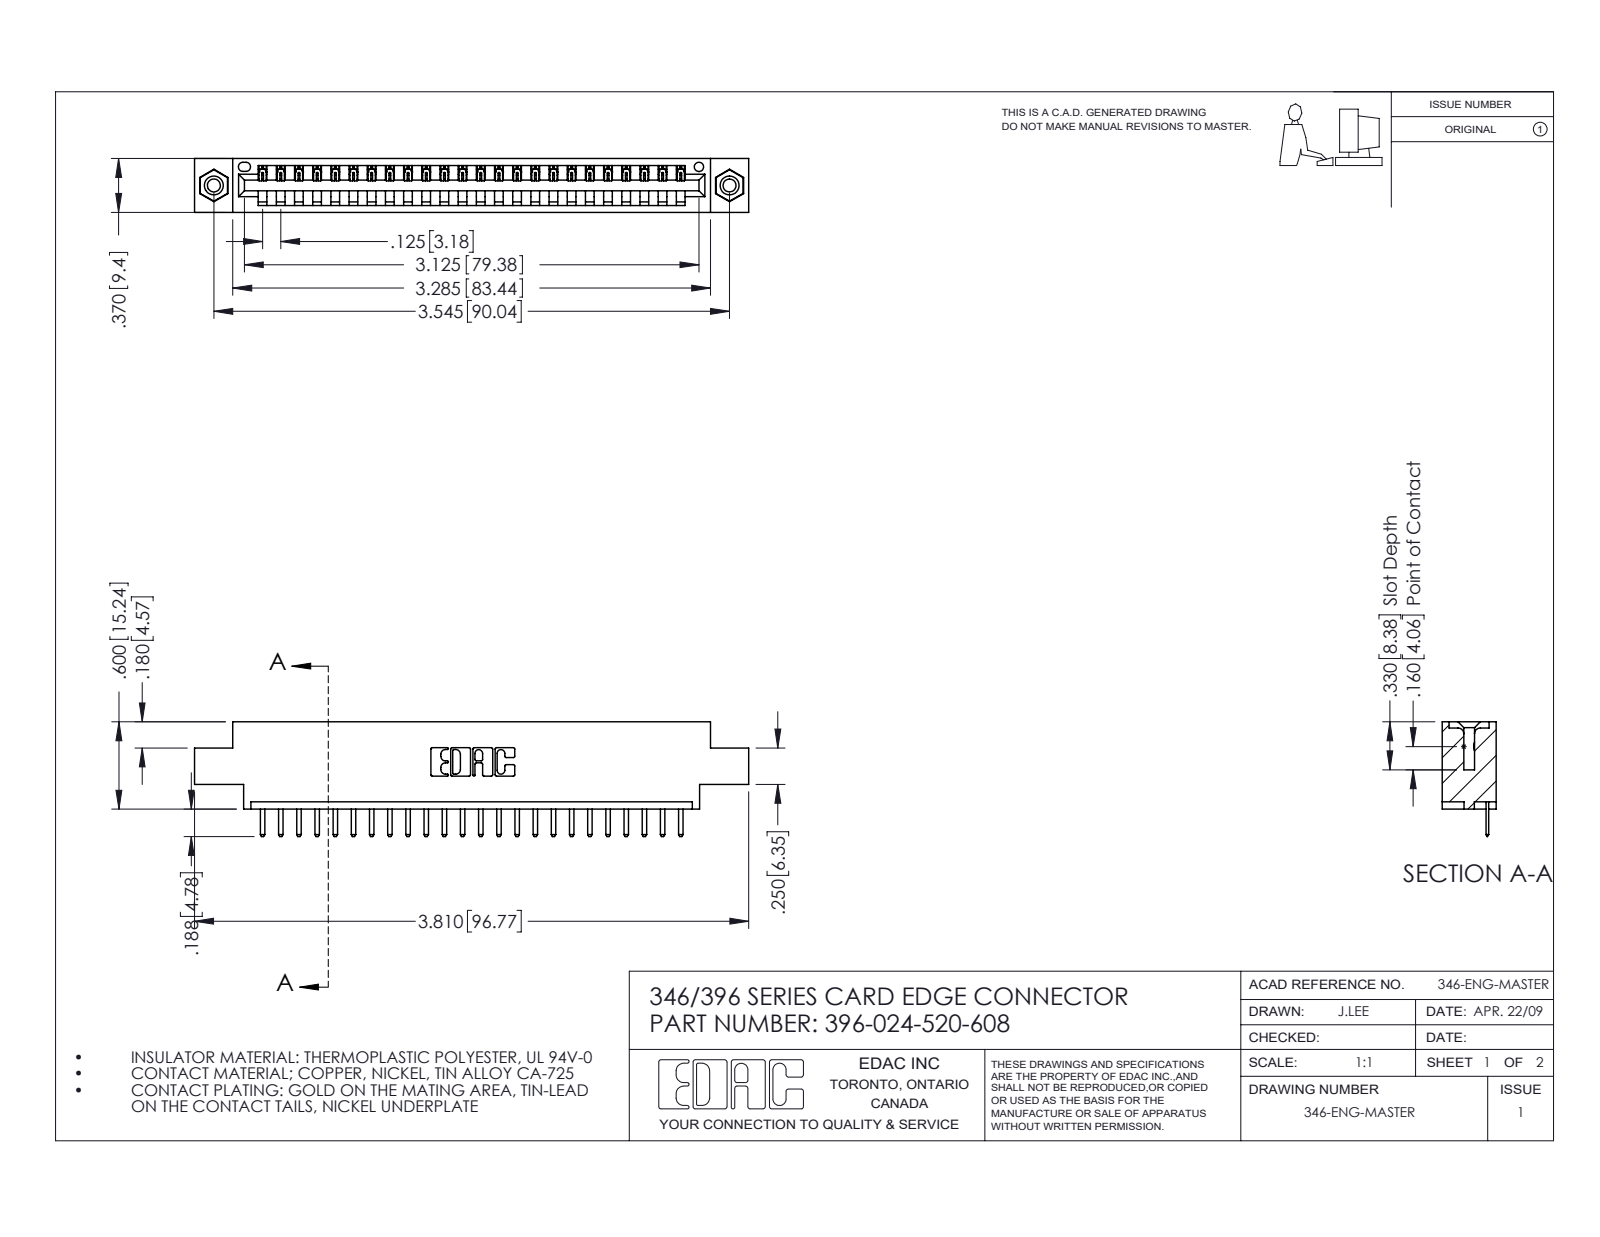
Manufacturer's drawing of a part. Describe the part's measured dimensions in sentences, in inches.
The part is named "396-024-520-608; 345-250-001_345-250-003-102; 345-292-001_345-293-120; 346 Part_0.170 Offset - 0.156 Dia-TI". Its 3-D file was written by "SolidWorks 2016 (CONFIG_CONTROL_DESIGN)". It is 27 solids with 1674 faces: 1120 planar, 538 cylindrical and 16 other. Overall it measures 3.81 by 0.788 by 0.37 inches. Its volume is 0.544 cubic inches and its surface area 16.88 square inches. Round holes: 2 of diameter 0.089, 2 of diameter 0.125, 2 of diameter 0.156, 1 of diameter 0.064. Round bosses or shafts: 2 of diameter 0.155. Partial cylindrical surfaces (rounded edges, fillets, slot ends): 50 of radius 0.01, 48 of radius 0.006, 22 of radius 0.01, 6 of radius 0.007, 6 of radius 0.031, 3 of radius 0.026, 2 of radius 0.031, 2 of radius 0.04. The main face-to-face distances are 0.048, 0.322, 0.37, 0.25, 0.222, 0.148, 0.1, 0.174, 0.072, 0.298. The hole center spacings are 0.246, 3.337, 3.545.
